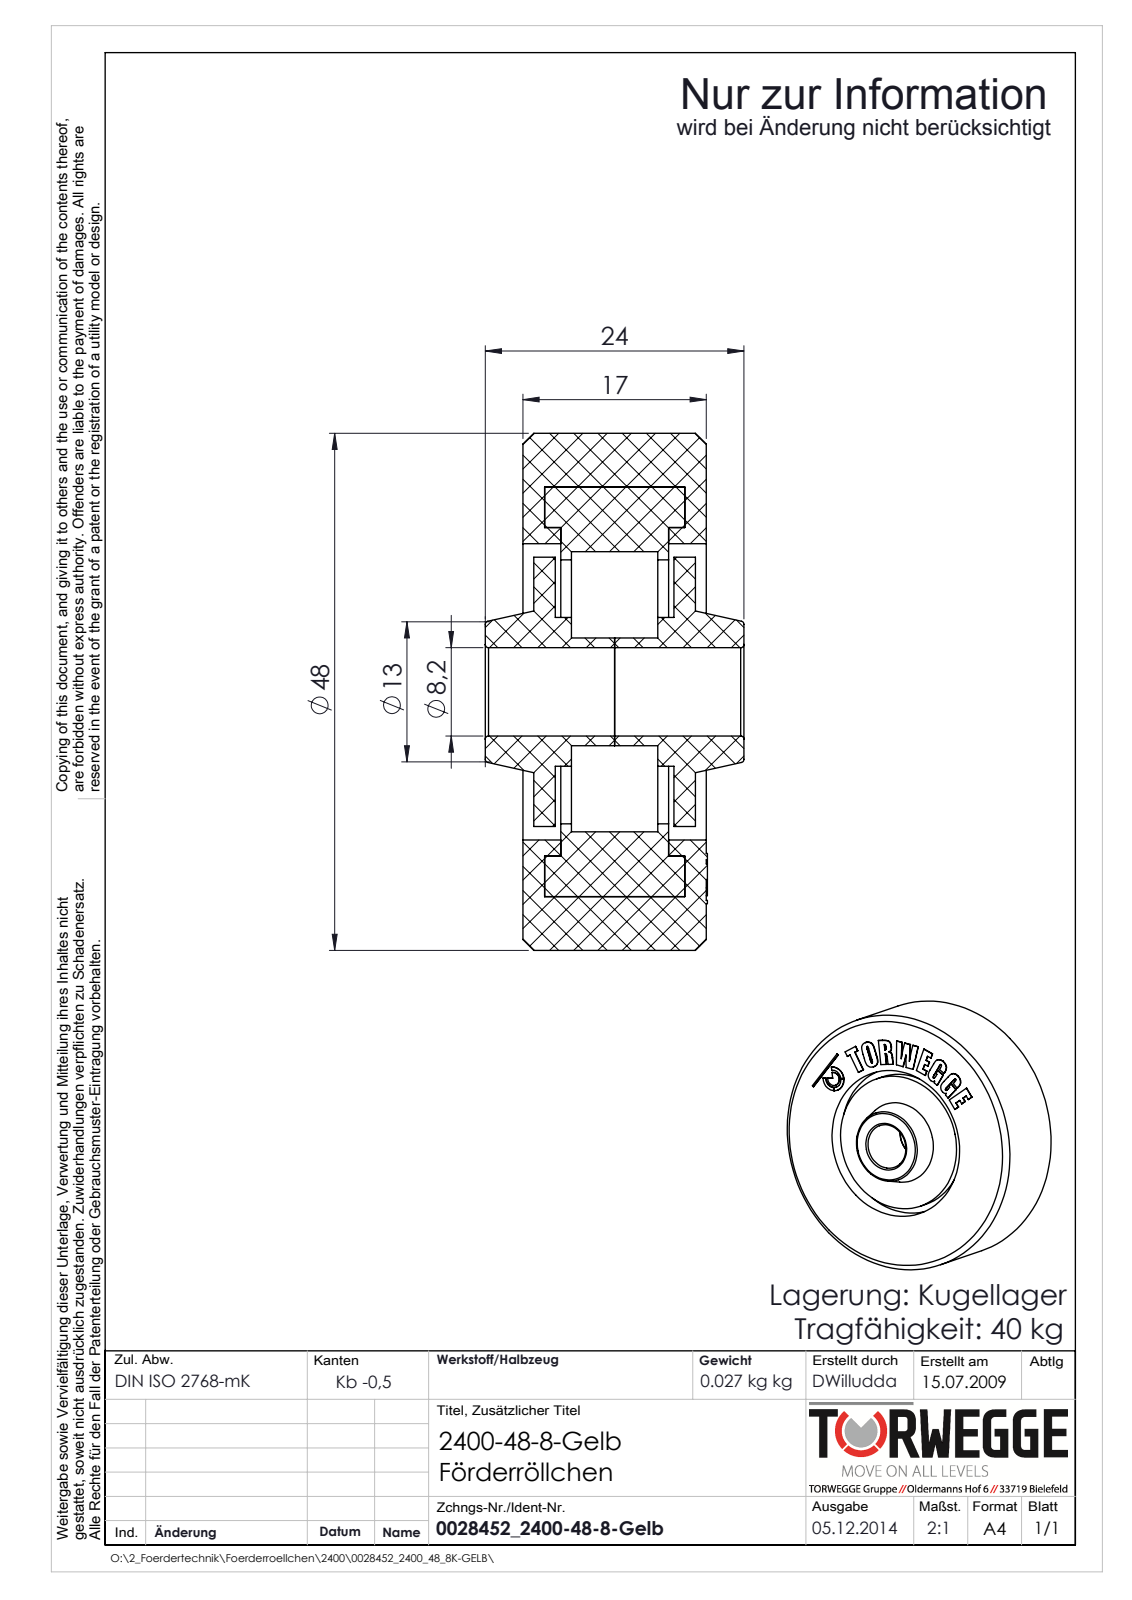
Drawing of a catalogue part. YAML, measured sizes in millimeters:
part_name: "Rillenkugellager_DIN625-6000-2RSR; 0028452_2400-48-8-Gelb; 0036031_2400-48-8K-KAPPE; 0028452-02 (+1 more)"
step_written_by: "SolidWorks 2016 (AUTOMOTIVE_DESIGN)"
units: millimeters
bodies: {solids: 4, faces: 254, planar: 133, cylindrical: 52, other: 69}
overall_size: [48, 48, 24]
volume: 24447
surface_area: 17920
round_holes:
  - {diameter: 8.2, count: 1}
  - {diameter: 10, count: 1}
  - {diameter: 22.5, count: 1}
  - {diameter: 24.5, count: 1}
  - {diameter: 26, count: 1}
  - {diameter: 27.5, count: 1}
  - {diameter: 30.5, count: 1}
  - {diameter: 38, count: 1}
round_bosses_or_shafts:
  - {diameter: 48, count: 1}
  - {diameter: 25, count: 1}
  - {diameter: 14.7, count: 1}
  - {diameter: 13.8, count: 1}
  - {diameter: 10.1, count: 1}
face_to_face_distances: [1, 2, 15, 3.5, 13, 1.5, 11.5, 12.5, 10.5, 14]
